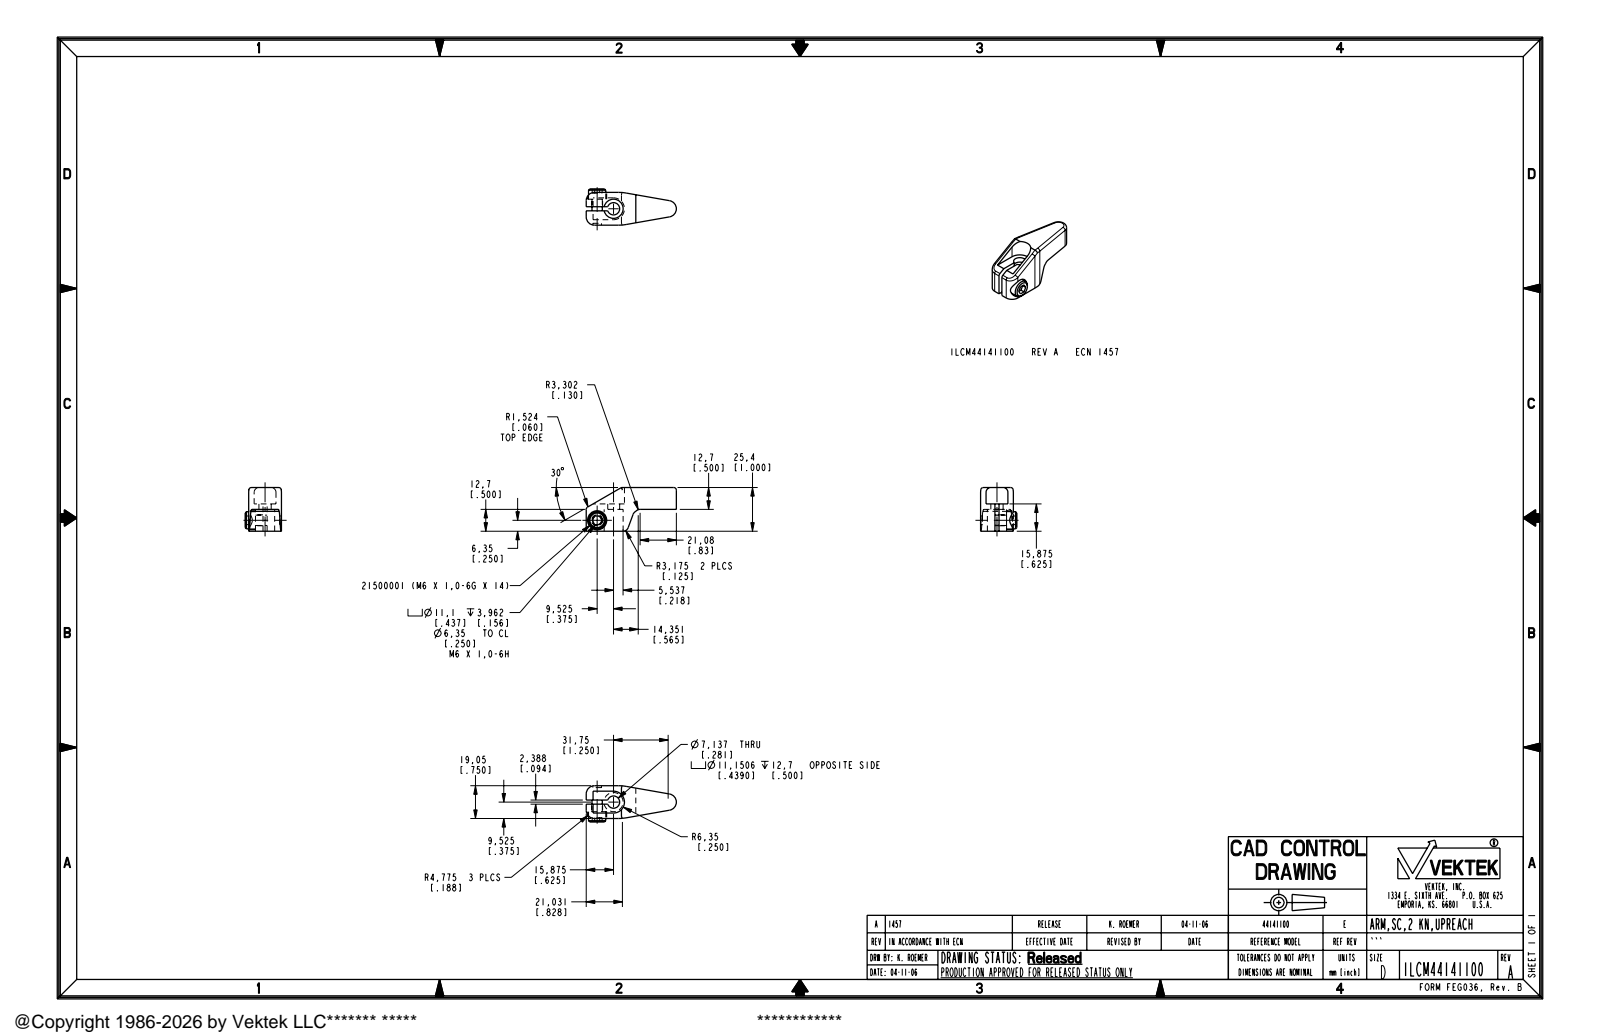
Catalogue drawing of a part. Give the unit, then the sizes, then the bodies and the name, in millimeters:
Units: millimetres
Overall size (bounding box): 52.4 × 25.4 × 21.09
Round holes (diameter × count): ⌀5.03 ×1, ⌀6.35 ×1, ⌀7.14 ×1, ⌀11.1 ×1, ⌀11.15 ×1
Round bosses / shafts (diameter × count): ⌀10 ×1, ⌀6 ×1
Partial cylindrical surfaces — rounded edges, fillets, slot ends (radius × count): R1.52 ×5, R4.78 ×3, R3.17 ×2, R25.4 ×2, R3.3 ×1, R6.35 ×1
Main face-to-face distances: 12.7, 25.4, 8.34, 10.72, 19.06, 9.53, 3.17, 15.87, 2.38, 3.18
Volume: 11 390 mm³ · Surface area: 5 144 mm²
Bodies: 1 solid, 66 faces (30 planar, 27 cylindrical, 9 other)
Part name (STEP PRODUCT): ILCM44141100
STEP written by: PRO/ENGINEER BY PARAMETRIC TECHNOLOGY CORPORATION, 2004290 (AUTOMOTIVE_DESIGN_CC2)
